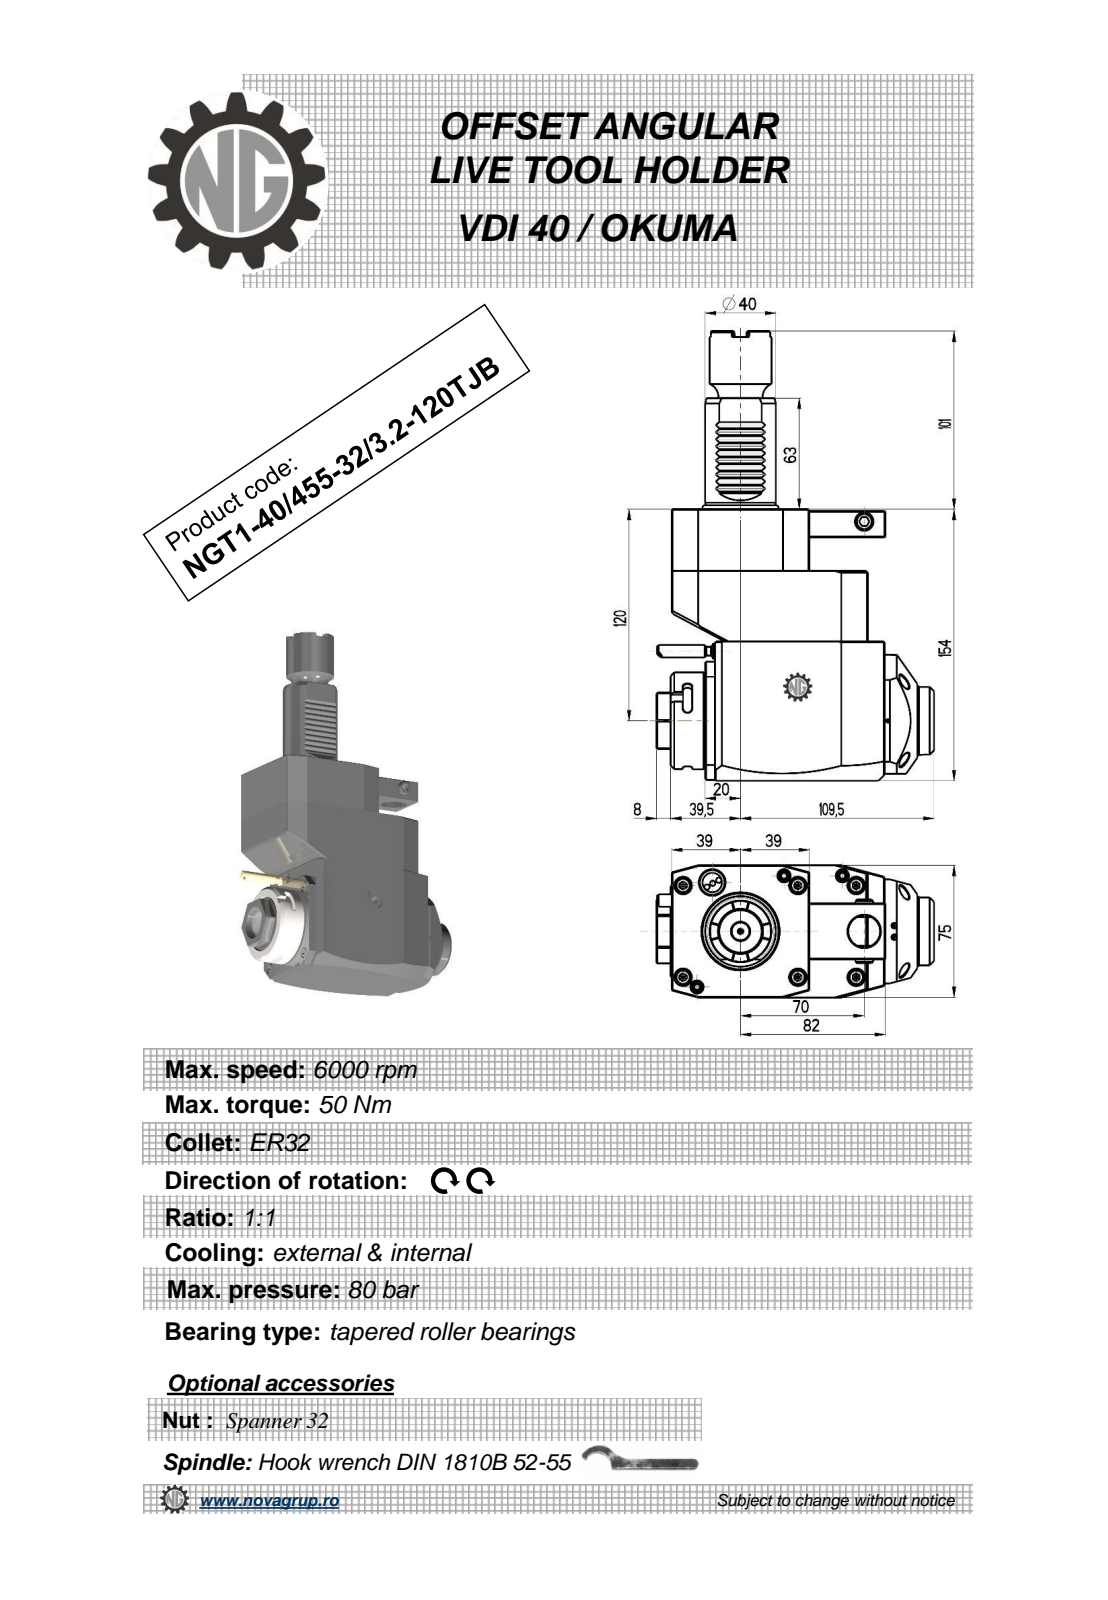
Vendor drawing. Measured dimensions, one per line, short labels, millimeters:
name: NGT1_40_455_32_3_2_120TJB
written by: PRO/ENGINEER BY PARAMETRIC TECHNOLOGY CORPORATION, 2010280 (CONFIG_CONTROL_DESIGN)
unit: mm
bodies: 1 solid, 379 faces (205 planar, 66 cylindrical, 108 other)
size: 255 × 157 × 75
volume: 1 321 000 mm³; area: 96 264 mm²
holes: 1× ⌀2.5, 1× ⌀3, 1× ⌀9.5, 1× ⌀18, 1× ⌀23, 1× ⌀25
bosses: 2× ⌀8.96, 1× ⌀55, 1× ⌀48, 1× ⌀40, 1× ⌀38.5, 1× ⌀35, 1× ⌀10, 1× ⌀7
rounds: 10× R0.3, 6× R2.5, 2× R180, 1× R0.5, 1× R4.25, 1× R24.5, 1× R37.5
face distances: 75, 154, 19, 59, 0.5, 111, 92, 35, 119, 53.5
hole spacings: 43.2, 70, 75.07, 112.5
